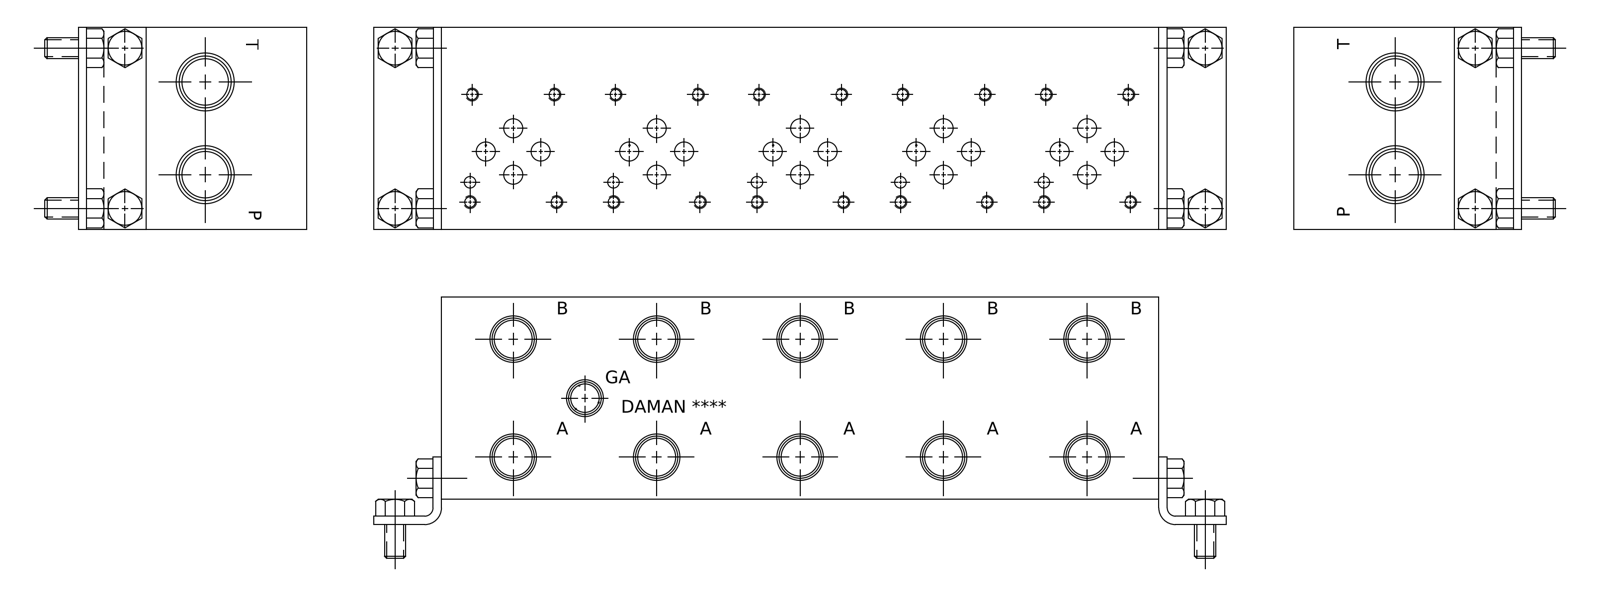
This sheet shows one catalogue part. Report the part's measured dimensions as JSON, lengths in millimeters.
{"part_name": "Part_DD03P052P_3D", "step_written_by": "Autodesk Inventor 2019 (AUTOMOTIVE_DESIGN)", "units": "millimeters", "bodies": {"solids": 1, "faces": 810, "planar": 444, "cylindrical": 103, "other": 263}, "overall_size": [269.88, 76.2, 76.2], "volume_mm3": 1498000, "surface_area_mm2": 115437, "round_holes": [[3.78, 20], [4.83, 20], [7.14, 15], [14.3, 10], [17.3, 10], [3.96, 5], [6.35, 5], [6.53, 2], [7.92, 2], [17.48, 2], [21.59, 2], [10.72, 1]], "face_to_face_distances": [76.2, 269.88, 11.73, 64.47, 15.37, 254.51, 1, 10.73, 75.2, 239.14], "hole_center_spacings": [107.95, 53.98, 53.97, 161.92, 161.93, 215.9, 56.73, 98]}
